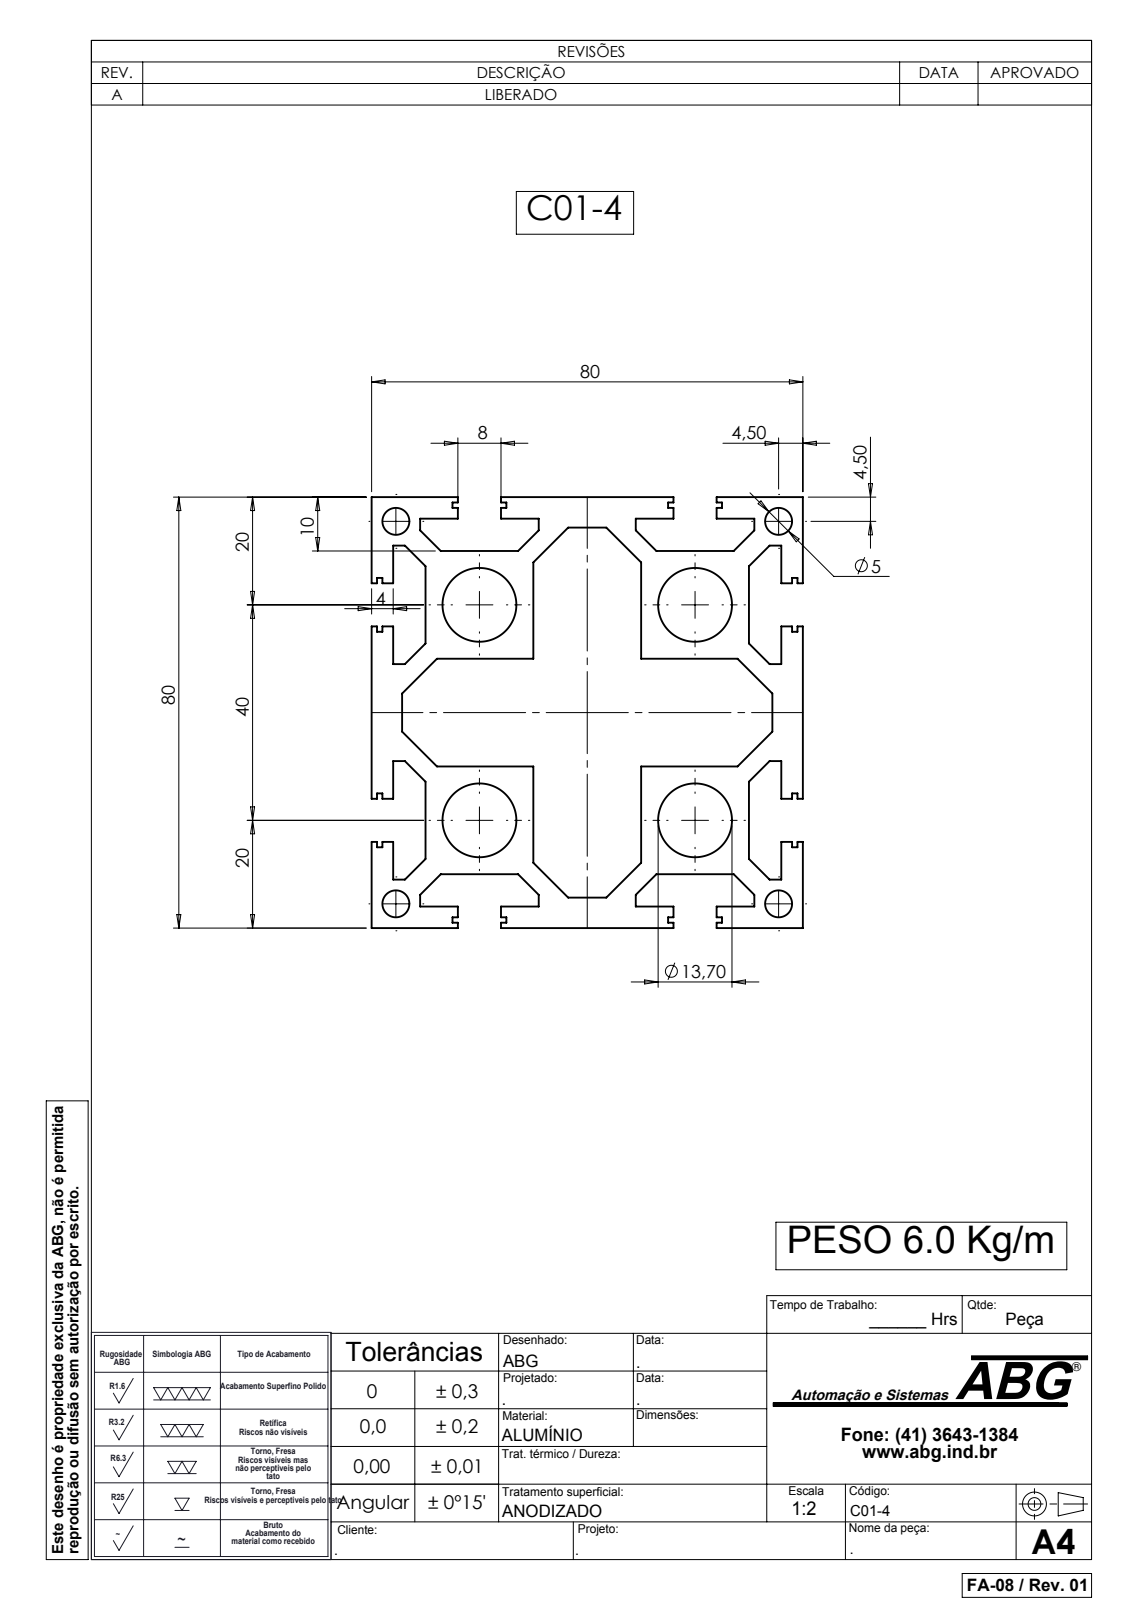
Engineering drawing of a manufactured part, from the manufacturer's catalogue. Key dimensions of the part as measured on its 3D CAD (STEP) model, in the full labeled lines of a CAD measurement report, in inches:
Part name (STEP PRODUCT): C01-4
STEP written by: SolidWorks 2007 (CONFIG_CONTROL_DESIGN)
Units: inches
Bodies: 1 solid, 186 faces (170 planar, 16 cylindrical, 0 other)
Overall size (bounding box): 236.22 × 3.15 × 3.15
Volume: 856.8 in³ · Surface area: 10 980 in²
Round holes (diameter × count): ⌀0.197 ×4, ⌀0.539 ×4
Main face-to-face distances: 0.787, 0.236, 1.575, 1.181, 1.969, 1.024, 1.811, 0.157, 3.15, 2.756
Hole centre spacings: 2.269, 0.863, 1.575, 2.795, 3.09, 2.227, 3.953
